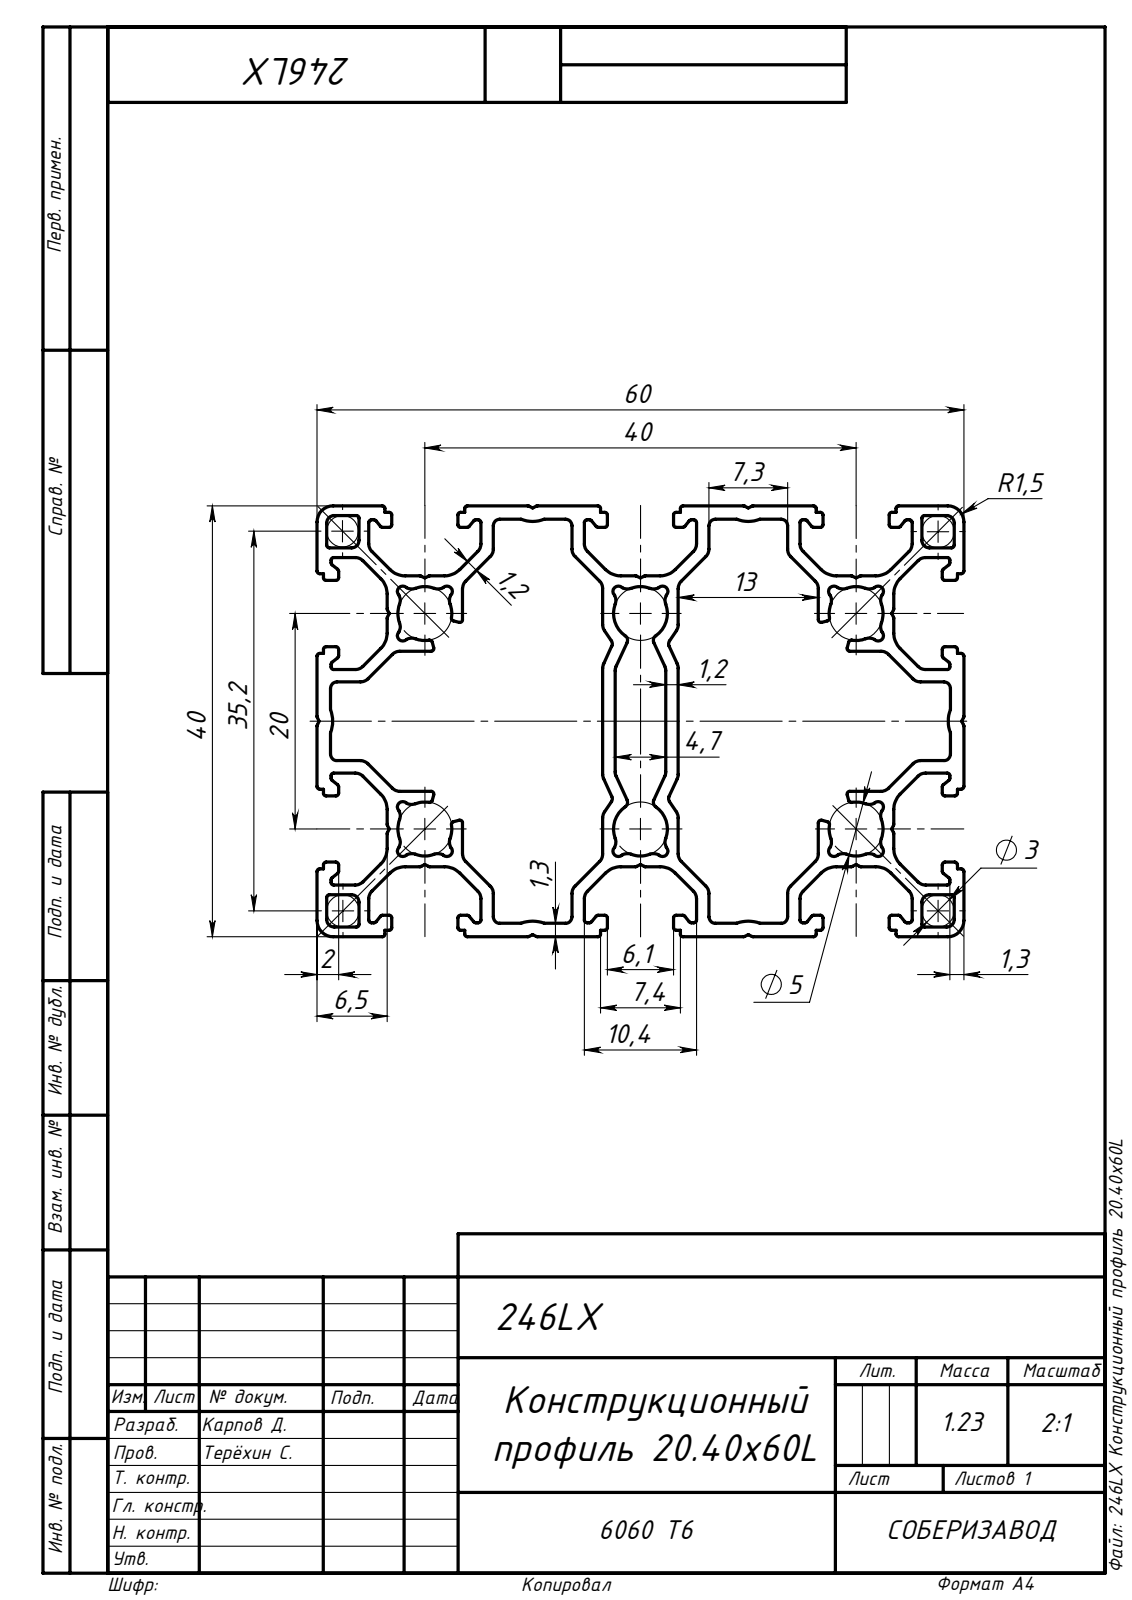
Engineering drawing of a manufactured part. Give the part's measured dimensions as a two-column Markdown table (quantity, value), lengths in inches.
| quantity | value |
| --- | --- |
| STEP written by | SolidWorks 2019 (AUTOMOTIVE_DESIGN) |
| units | inches |
| bodies | 1 solid, 686 faces (322 planar, 364 cylindrical, 0 other) |
| overall size | 39.37 × 2.362 × 1.575 |
| volume | 27.86 in³ |
| surface area | 1 212 in² |
| partial cylindrical surfaces (radius × count) | 0.01 × 176, 0.039 × 88, 0.02 × 24, 0.079 × 20, 0.024 × 12, 0.028 × 8, 0.098 × 6, 0.118 × 6 |
| main face-to-face distances | 0.045, 0.787, 1.319, 1.043, 1.575, 0.557, 0.276, 0.445, 0.343, 1.115 |
